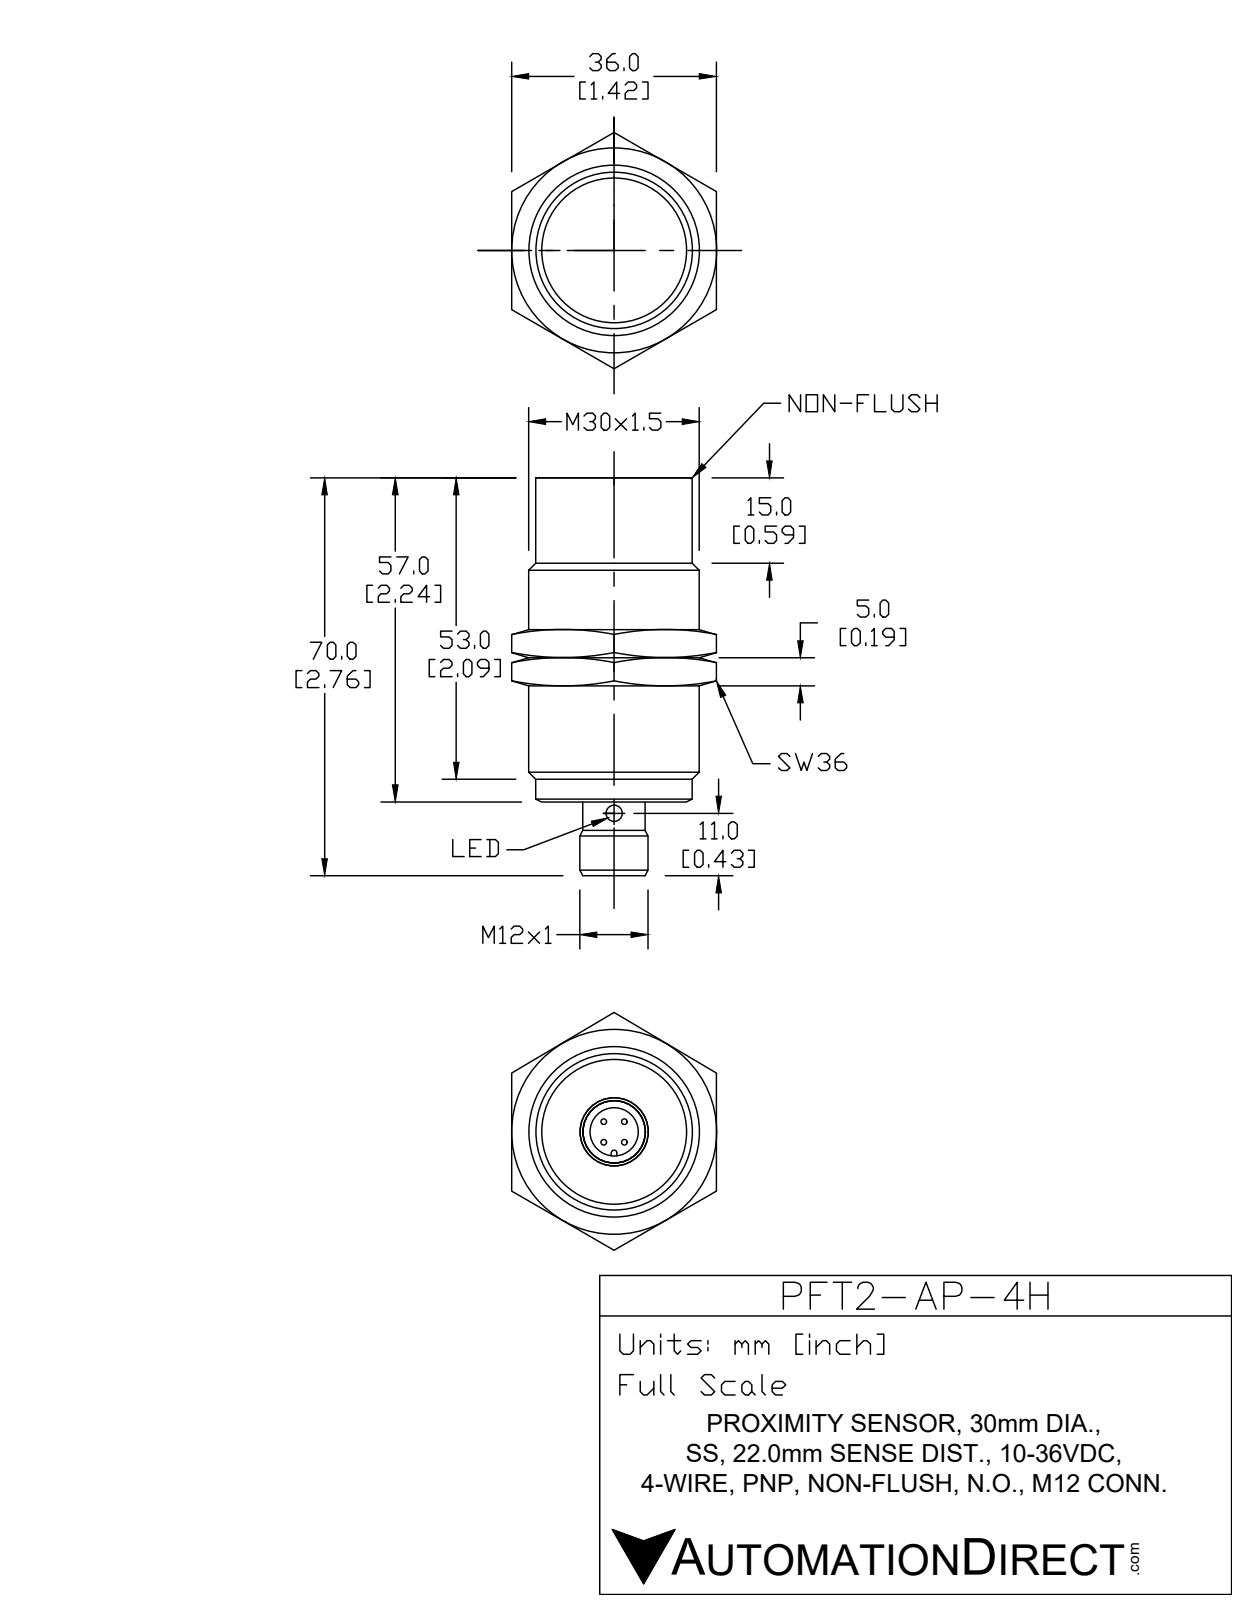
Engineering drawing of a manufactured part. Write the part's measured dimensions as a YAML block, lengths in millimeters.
part_name: "PFT2-AP-4H"
step_written_by: "SolidWorks 2017 (AUTOMOTIVE_DESIGN)"
units: millimeters
bodies: {solids: 3, faces: 96, planar: 24, cylindrical: 32, other: 40}
overall_size: [70, 41.6, 36]
volume: 43840
surface_area: 11080
round_holes:
  - {diameter: 2, count: 2}
  - {diameter: 28.4, count: 1}
round_bosses_or_shafts:
  - {diameter: 30, count: 1}
  - {diameter: 28.2, count: 1}
  - {diameter: 26, count: 1}
  - {diameter: 12, count: 1}
  - {diameter: 10.8, count: 1}
  - {diameter: 9, count: 1}
partial_cylinders:
  - {radius: 0.6, count: 1}
face_to_face_distances: [35, 5, 36, 22, 57, 10, 30, 17, 40, 27]
